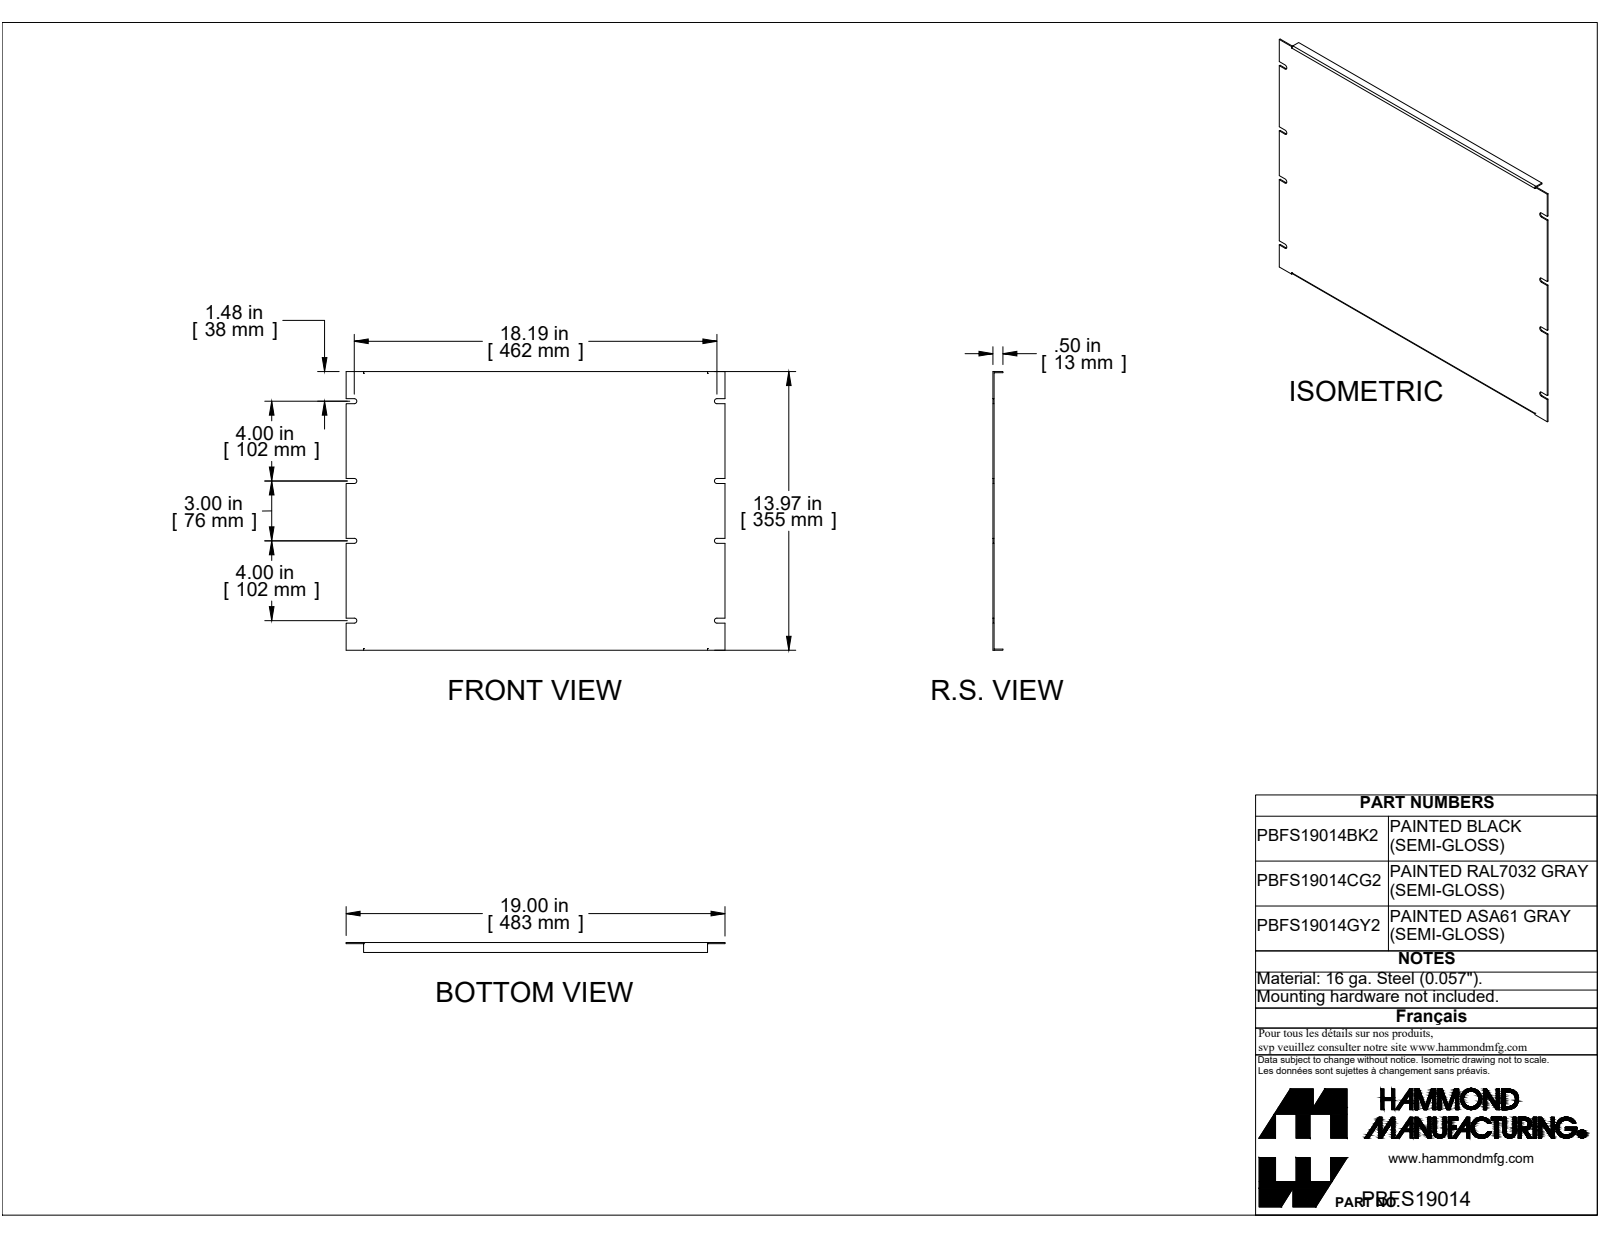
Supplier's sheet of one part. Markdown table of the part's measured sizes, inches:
| quantity | value |
| --- | --- |
| part name | PBFS19014 |
| STEP written by | SolidWorks 2019 (CONFIG_CONTROL_DESIGN) |
| units | inches |
| bodies | 1 solid, 62 faces (50 planar, 12 cylindrical, 0 other) |
| overall size | 19 × 13.968 × 0.5 |
| volume | 15.89 in³ |
| surface area | 562 in² |
| partial cylindrical surfaces (radius × count) | 0.125 × 8, 0.029 × 2, 0.086 × 2 |
| main face-to-face distances | 0.057, 0.057, 13.911, 13.968, 13.854, 0.5, 0.443, 19, 0.25, 4 |
